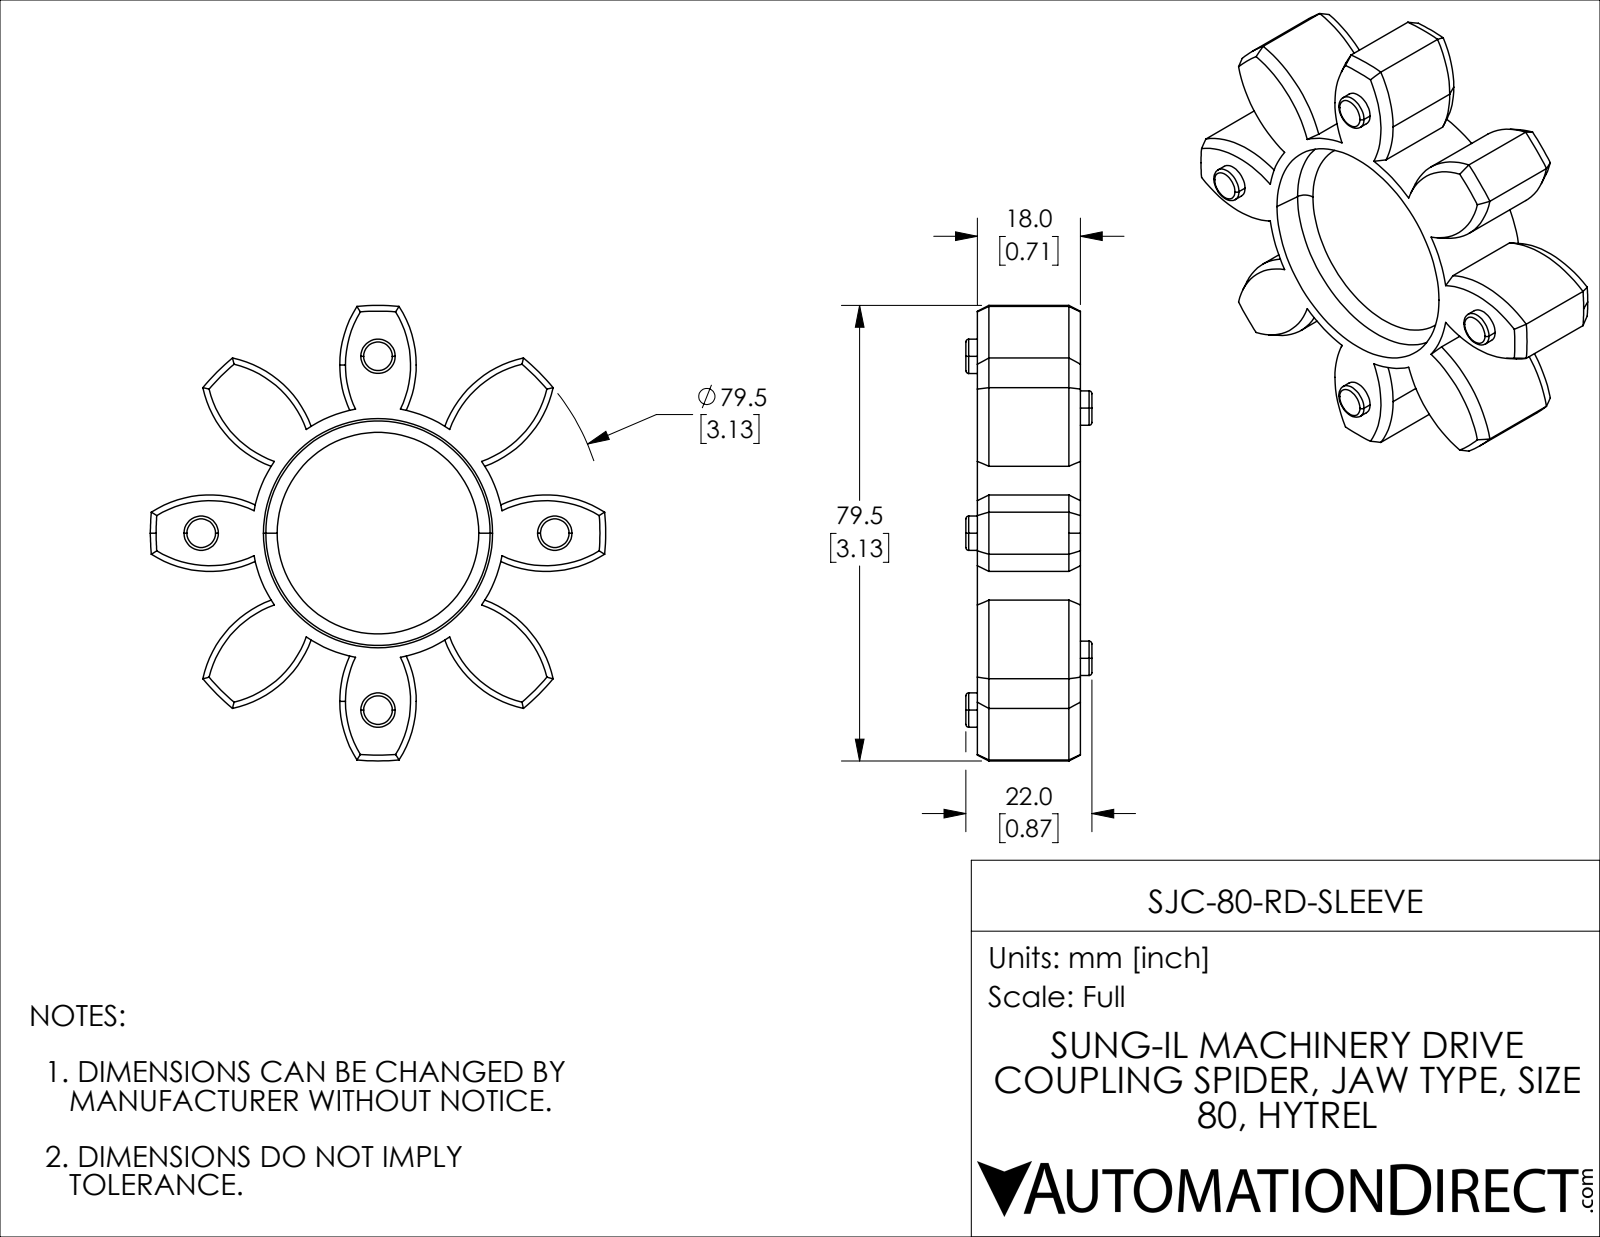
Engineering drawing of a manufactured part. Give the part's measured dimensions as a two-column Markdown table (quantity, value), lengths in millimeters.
| quantity | value |
| --- | --- |
| part name | SJC-80-RD-SLEEVE |
| STEP written by | SolidWorks 2021 (CONFIG_CONTROL_DESIGN) |
| units | millimeters |
| bodies | 1 solid, 141 faces (12 planar, 51 cylindrical, 78 other) |
| overall size | 79.5 × 79.5 × 22 |
| volume | 41 732 mm³ |
| surface area | 15 001 mm² |
| round bosses / shafts (diameter × count) | 6 × 8 |
| partial cylindrical surfaces (radius × count) | 18.84 × 8, 22 × 1, 39.75 × 1 |
| main face-to-face distances | 6.5, 11.5, 18, 5, 2, 8.5, 13.5, 20, 22 |
